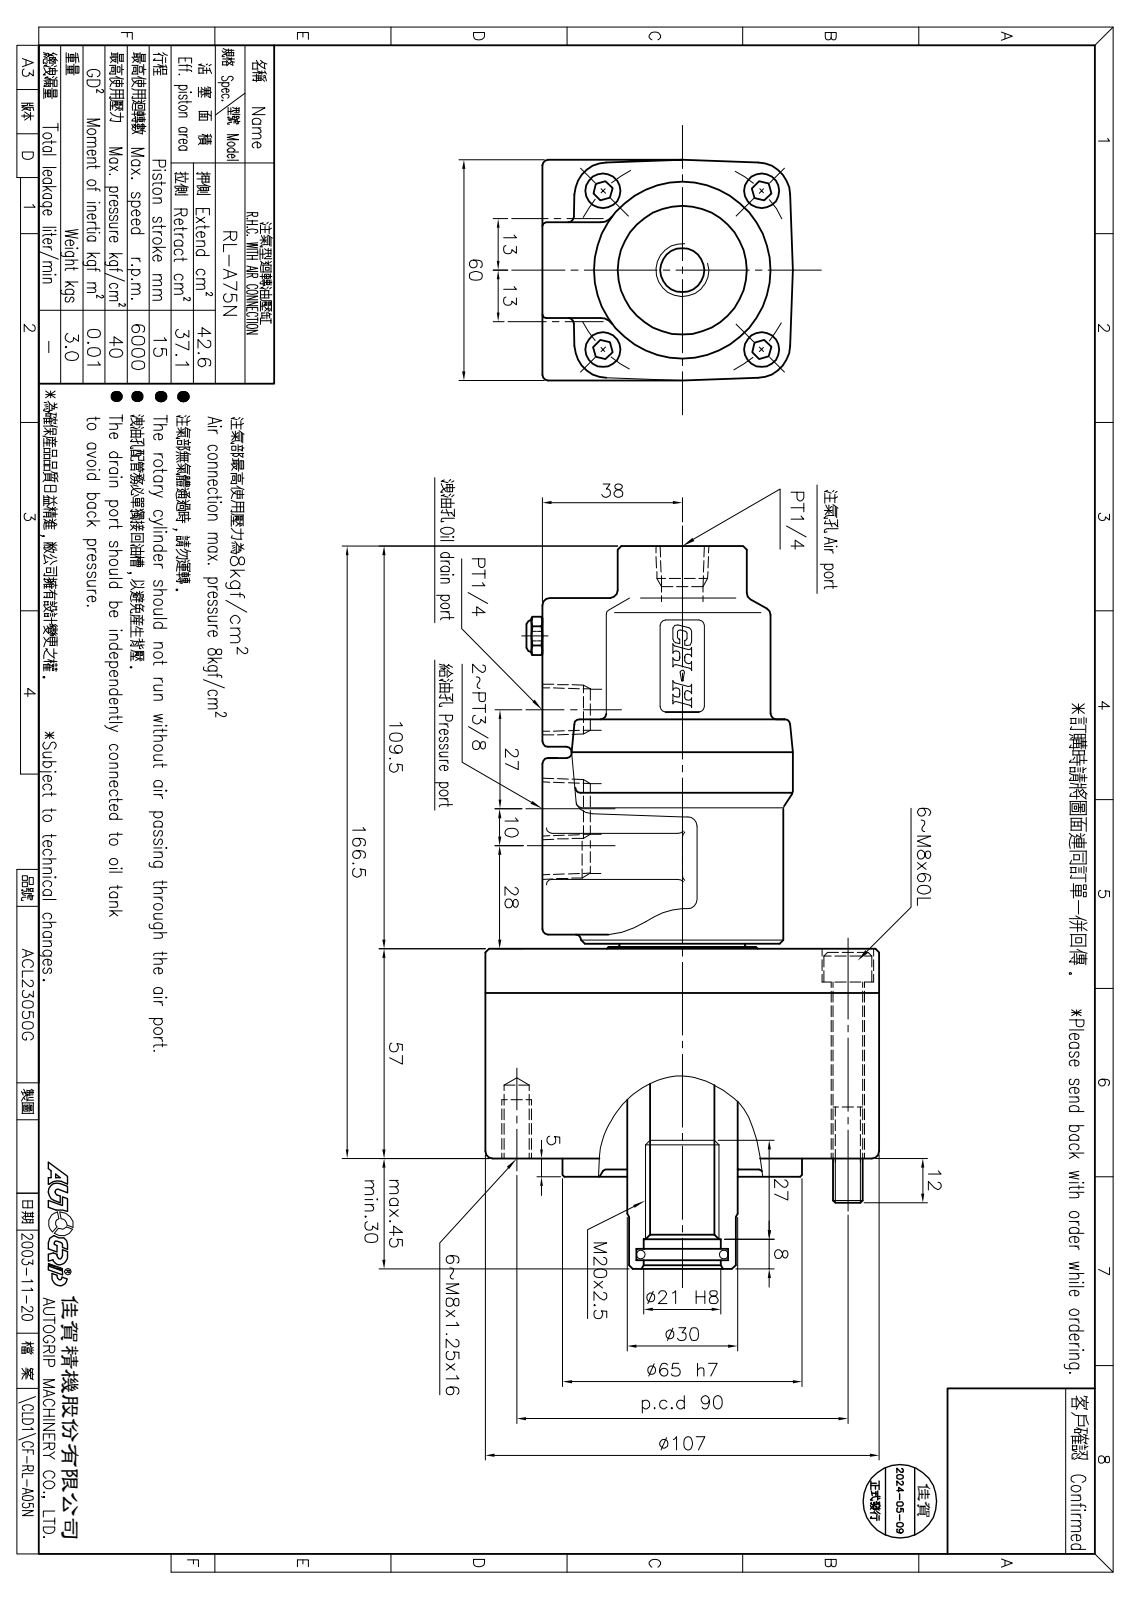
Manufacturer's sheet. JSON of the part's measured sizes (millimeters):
{"part_name": "RK-75缸體; RL-A100N消音器; RL-A75N組合件; RL-75活塞", "step_written_by": "SolidWorks 2010 (CONFIG_CONTROL_DESIGN)", "units": "millimeters", "bodies": {"solids": 6, "faces": 415, "planar": 90, "cylindrical": 154, "other": 171}, "overall_size": [196.5, 107, 107], "volume_mm3": 717225, "surface_area_mm2": 140986, "round_holes": [[6.8, 6], [8, 6], [9, 6], [14, 6], [11.2, 2], [14.7, 2], [2.6, 1], [4.1, 1], [5, 1], [17.5, 1], [20, 1], [21, 1]], "round_bosses_or_shafts": [[107, 1], [75, 1], [65, 1], [55, 1], [48, 1], [35, 1], [29, 1], [3.8, 1]], "partial_cylinders_radius": [[1.5, 24], [6, 4], [9, 4], [2, 3], [5, 2], [15, 2]], "face_to_face_distances": [15, 7, 30, 12, 19, 53.5, 65.5, 72.5, 45, 57], "hole_center_spacings": [45, 86.94, 23.29, 63.65, 77.94, 23.3, 63.64, 77.95]}
